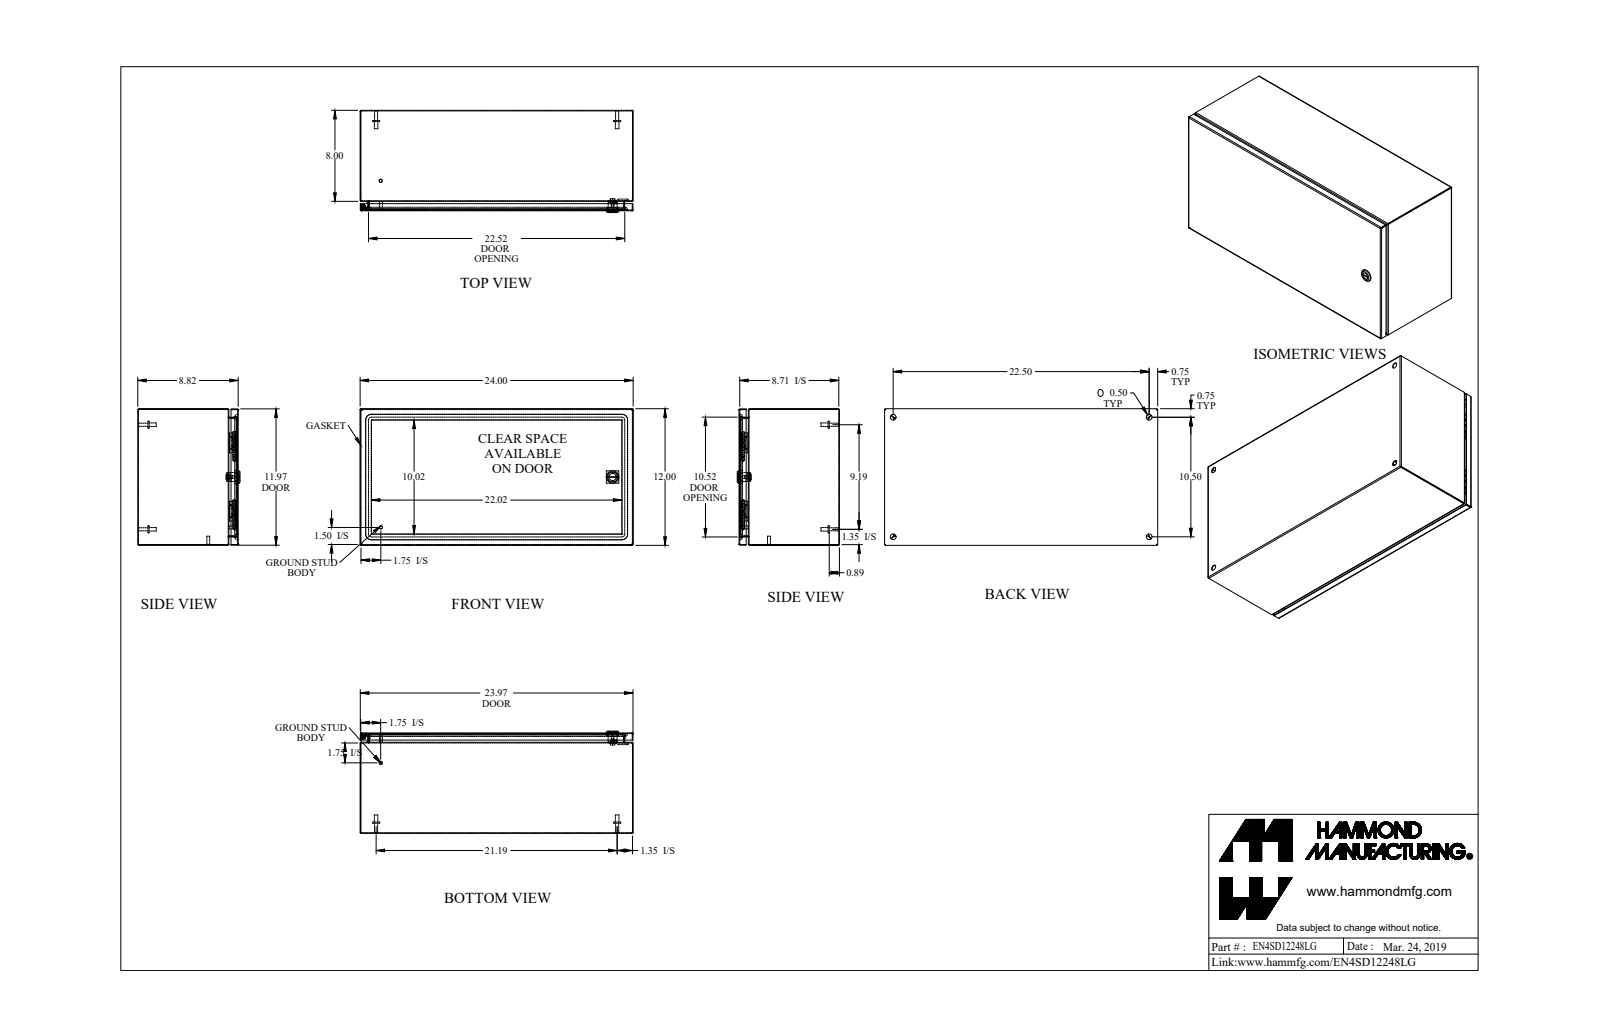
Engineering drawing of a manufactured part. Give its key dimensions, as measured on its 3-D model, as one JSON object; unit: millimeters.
{"part_name": "EN4SD12248LG_Default", "step_written_by": "SolidWorks 2019 (CONFIG_CONTROL_DESIGN)", "units": "millimeters", "bodies": {"solids": 21, "faces": 634, "planar": 285, "cylindrical": 213, "other": 136}, "overall_size": [609.6, 304.8, 228.1], "volume_mm3": 1324000, "surface_area_mm2": 1770000, "round_holes": [[12.7, 4], [4.4, 1], [5.9, 1], [6.1, 1], [6.1, 1], [15.9, 1], [19.9, 1]], "round_bosses_or_shafts": [[15.9, 4], [8, 4], [6.9, 4], [7.1, 2], [6.4, 2], [27.9, 1], [13.3, 1], [11.6, 1]], "partial_cylinders_radius": [[0.7, 21], [2.2, 21], [6.4, 16], [482.6, 8], [0.2, 4], [1.6, 4], [12.7, 4], [3.2, 2]], "face_to_face_distances": [1.4, 222.6, 303.4, 221.2, 224.1, 301.9, 304.8, 608.2, 606.7, 609.6], "hole_center_spacings": [266.7, 560.7, 571.5, 630.7, 136, 136]}
